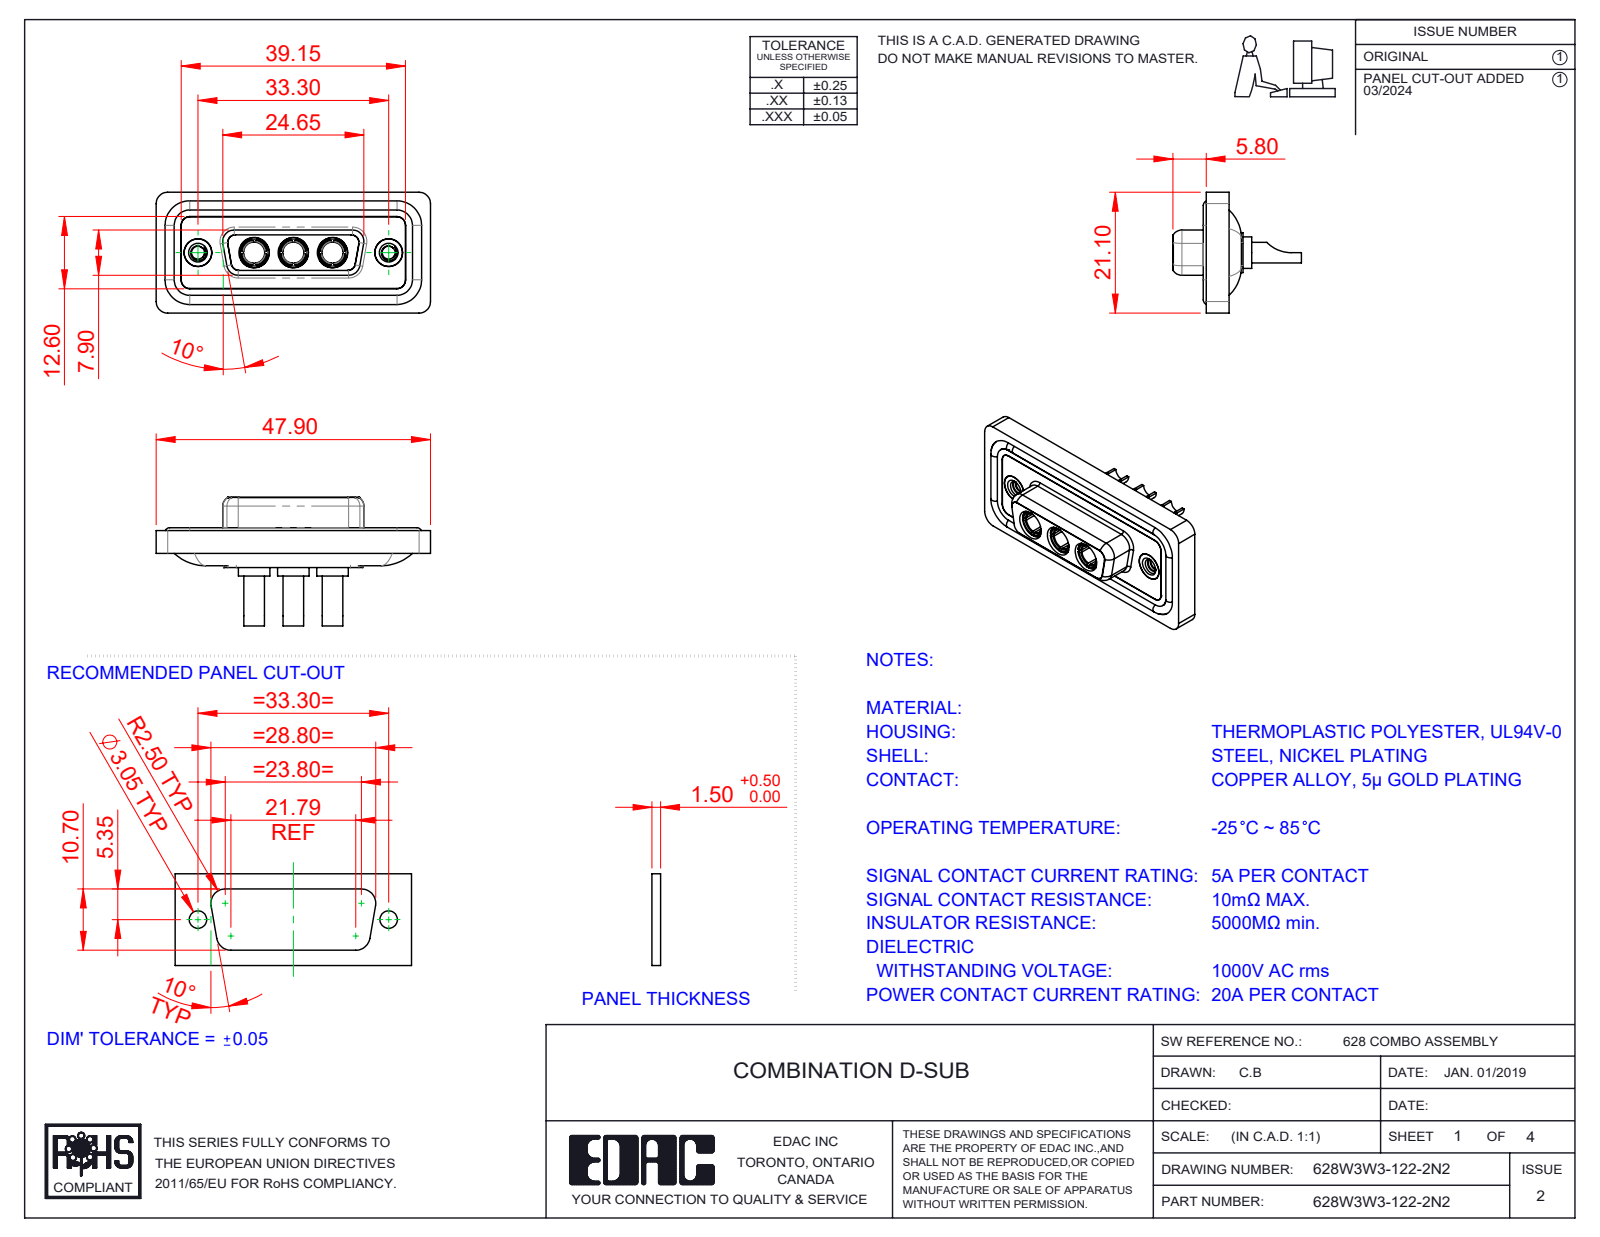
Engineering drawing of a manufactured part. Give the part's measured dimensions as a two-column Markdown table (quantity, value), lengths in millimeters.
| quantity | value |
| --- | --- |
| part name | 628Combo Waterproof Housing_15 Contacts; Power Socket_20A SC; 628Combo Housing_3W3; 628W3W3-122-2N2 (+3 more) |
| STEP written by | SolidWorks 2023 (CONFIG_CONTROL_DESIGN) |
| units | millimeters |
| bodies | 13 solids, 626 faces (201 planar, 266 cylindrical, 159 other) |
| overall size | 47.9 × 22.45 × 21.1 |
| volume | 6 065 mm³ |
| surface area | 9 986 mm² |
| round holes (diameter × count) | 4.85 × 5, 2.7 × 3, 3.7 × 3, 5.3 × 3, 2.26 × 2, 4 × 2, 4.05 × 2, 5 × 2 |
| round bosses / shafts (diameter × count) | 1.6 × 4, 5.5 × 3, 5.2 × 3, 4.96 × 3, 4.75 × 3, 3.75 × 3, 3.6 × 3, 4.95 × 2 |
| partial cylindrical surfaces (radius × count) | 1.5 × 22, 2 × 20, 1.35 × 12, 1.6 × 8, 0.25 × 4, 0.5 × 4, 0.6 × 4, 0.65 × 4 |
| main face-to-face distances | 0.4, 1.8, 1.6, 0.5, 7.45, 1.1, 2.9, 5.65, 7.05, 6.6 |
| hole center spacings | 6.85, 9.8, 16.65, 23.5, 13.7, 33.3 |
